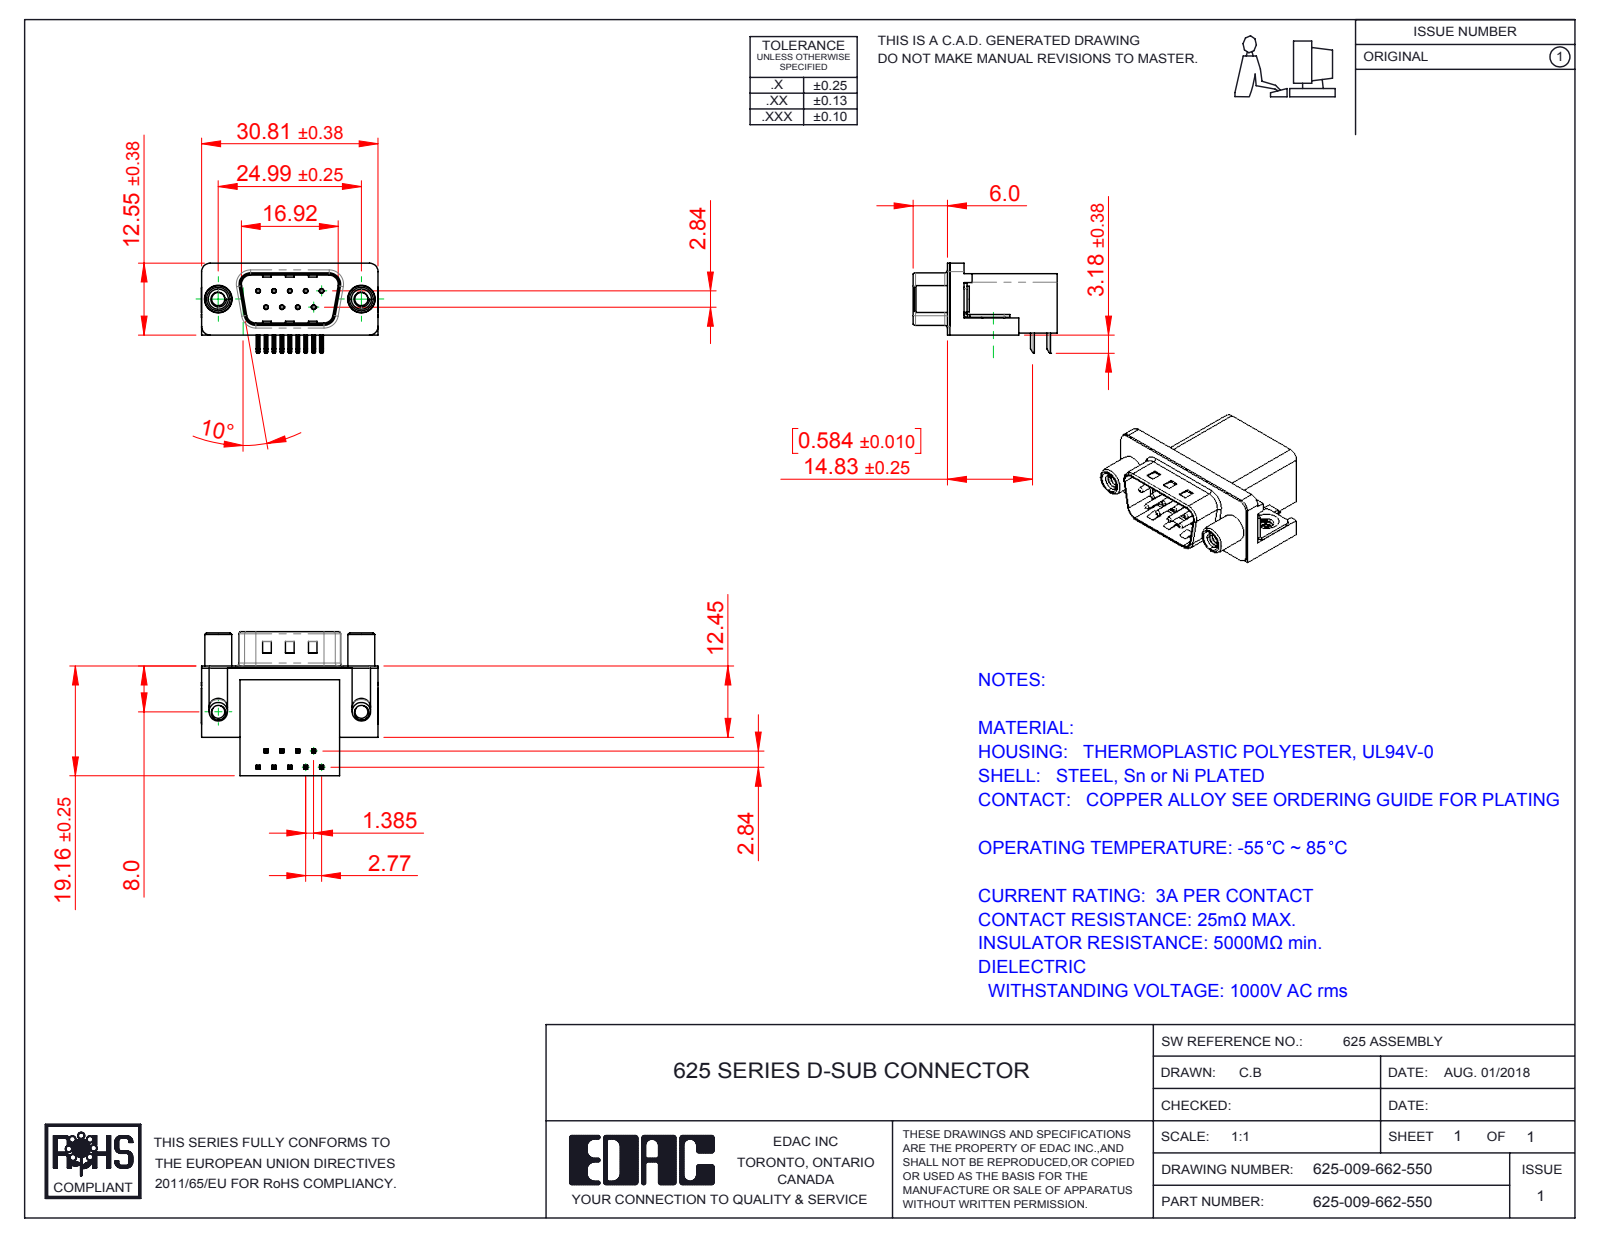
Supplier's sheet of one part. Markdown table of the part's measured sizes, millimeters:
| quantity | value |
| --- | --- |
| part name | 625 Contact Top; 625 Shell_9 Socket; 625 Contact Bottom; 625 Housing_9 Socket (+3 more) |
| STEP written by | SolidWorks 2016 (CONFIG_CONTROL_DESIGN) |
| units | millimeters |
| bodies | 15 solids, 1019 faces (567 planar, 337 cylindrical, 115 other) |
| overall size | 30.89 × 25.16 × 15.73 |
| volume | 4 577 mm³ |
| surface area | 5 230 mm² |
| round holes (diameter × count) | 0.35 × 9, 0.8 × 9, 2.26 × 2, 2.3 × 2, 3.1 × 2, 4 × 2, 4.8 × 2, 5 × 2 |
| round bosses / shafts (diameter × count) | 0.75 × 9, 4.9 × 2, 4.7 × 2, 4.5 × 2, 3.85 × 2, 3.26 × 2 |
| partial cylindrical surfaces (radius × count) | 0.25 × 36, 0.12 × 18, 1 × 16, 0.5 × 9, 1.5 × 8, 1.6 × 8, 0.9 × 4, 2 × 4 |
| main face-to-face distances | 0.4, 10.34, 18.76, 19.16, 16.26, 2.5, 2.9, 0.35, 10.69, 6.7 |
| hole center spacings | 3.16, 2.77, 5.54, 5.03, 5.04, 8.31, 7.48, 7.49 |
